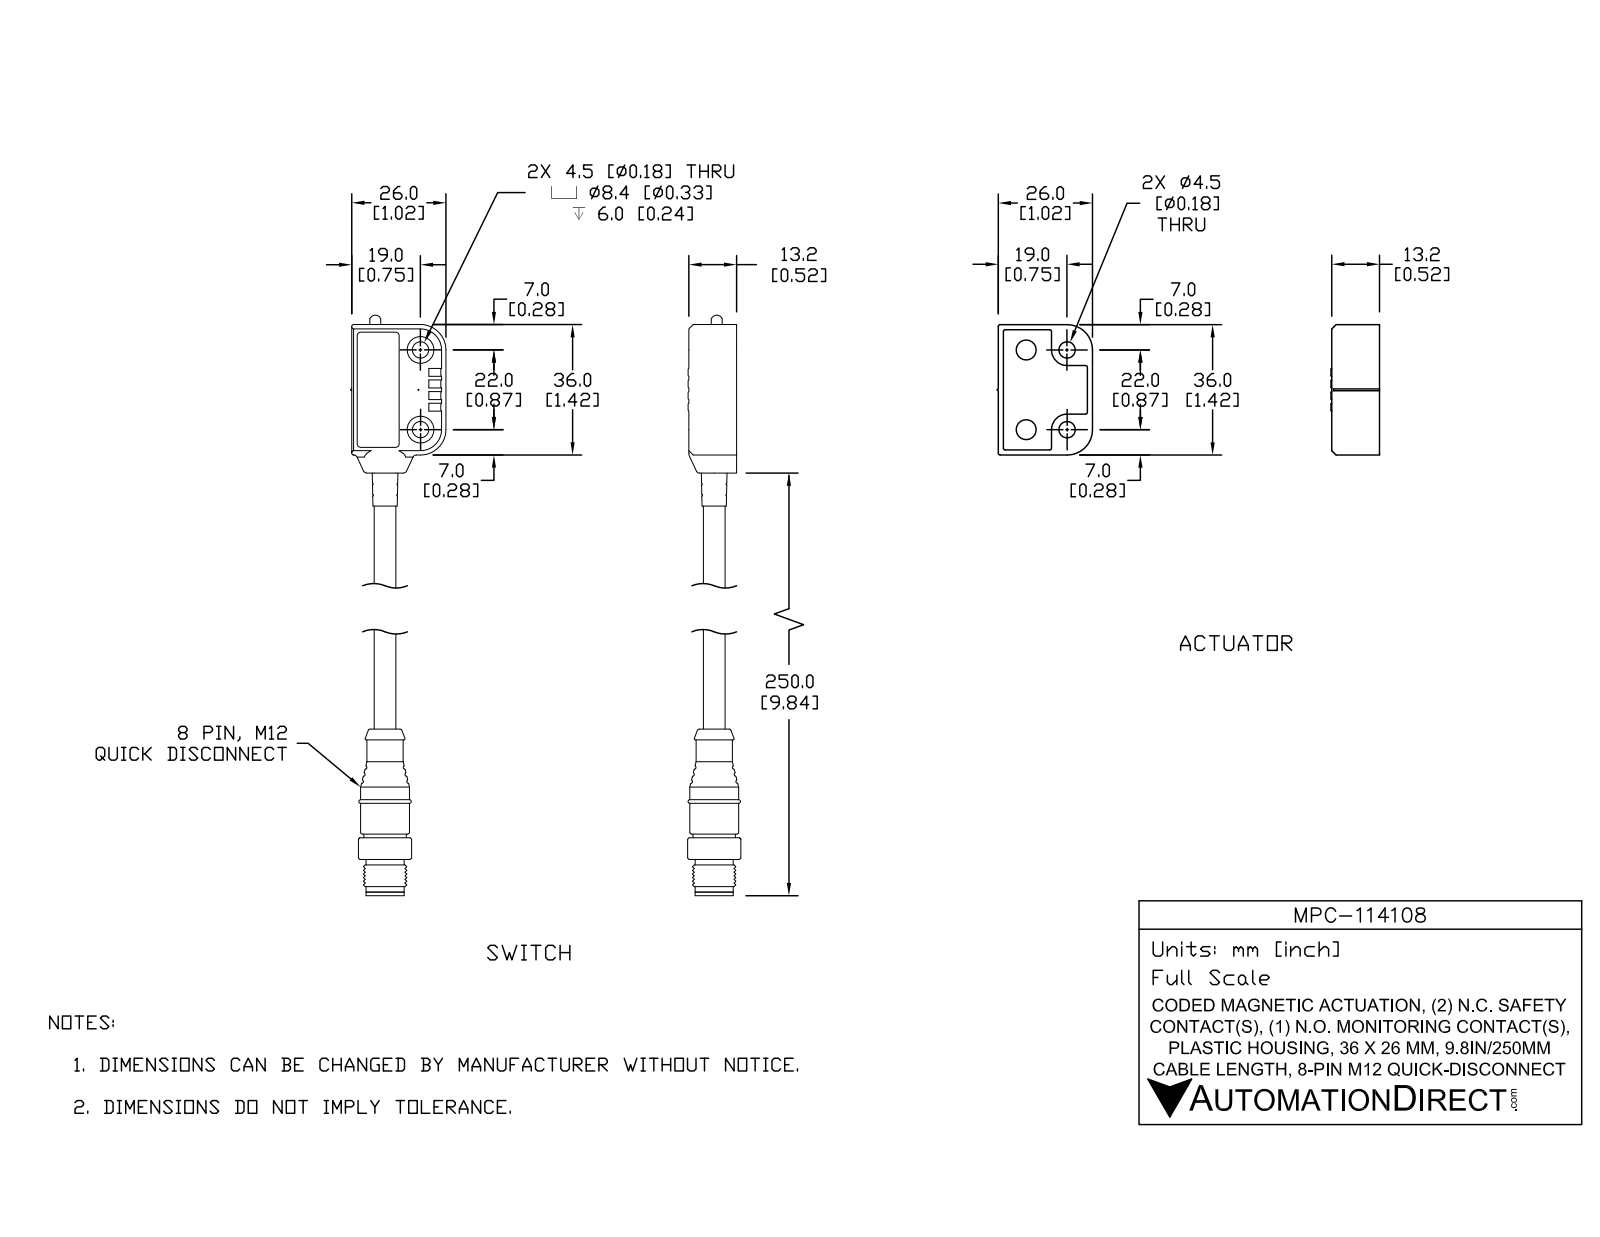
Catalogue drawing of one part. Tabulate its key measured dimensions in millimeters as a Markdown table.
| quantity | value |
| --- | --- |
| part name | MPC-114108_2; MPC-114108; MPC-114108_1 |
| STEP written by | SolidWorks 2017 (AUTOMOTIVE_DESIGN) |
| units | millimeters |
| bodies | 11 solids, 1430 faces (610 planar, 462 cylindrical, 358 other) |
| overall size | 293.6 × 53 × 14.7 |
| volume | 23 710 mm³ |
| surface area | 23 960 mm² |
| round holes (diameter × count) | 4.5 × 4, 8.4 × 4, 5 × 2, 2.5 × 1, 3 × 1, 5 × 1, 5.9 × 1, 6.2 × 1, 7.4 × 1, 8.3 × 1, 11.8 × 1 |
| round bosses / shafts (diameter × count) | 0.8 × 10, 6 × 2, 5 × 2, 2.3 × 2, 2 × 2, 13.5 × 1, 11.7 × 1, 10.5 × 1 |
| partial cylindrical surfaces (radius × count) | 0.5 × 86, 0.3 × 35, 0.2 × 30, 0.1 × 17, 1 × 13, 4.3 × 4, 5.1 × 4, 7 × 4 |
| main face-to-face distances | 1.4, 12.9, 11.4, 11.7, 1.5, 1.2, 27, 12.6, 11.3, 0.8 |
| hole center spacings | 22, 11, 11.3, 24.7, 27.7, 29.3, 35.4, 39 |
